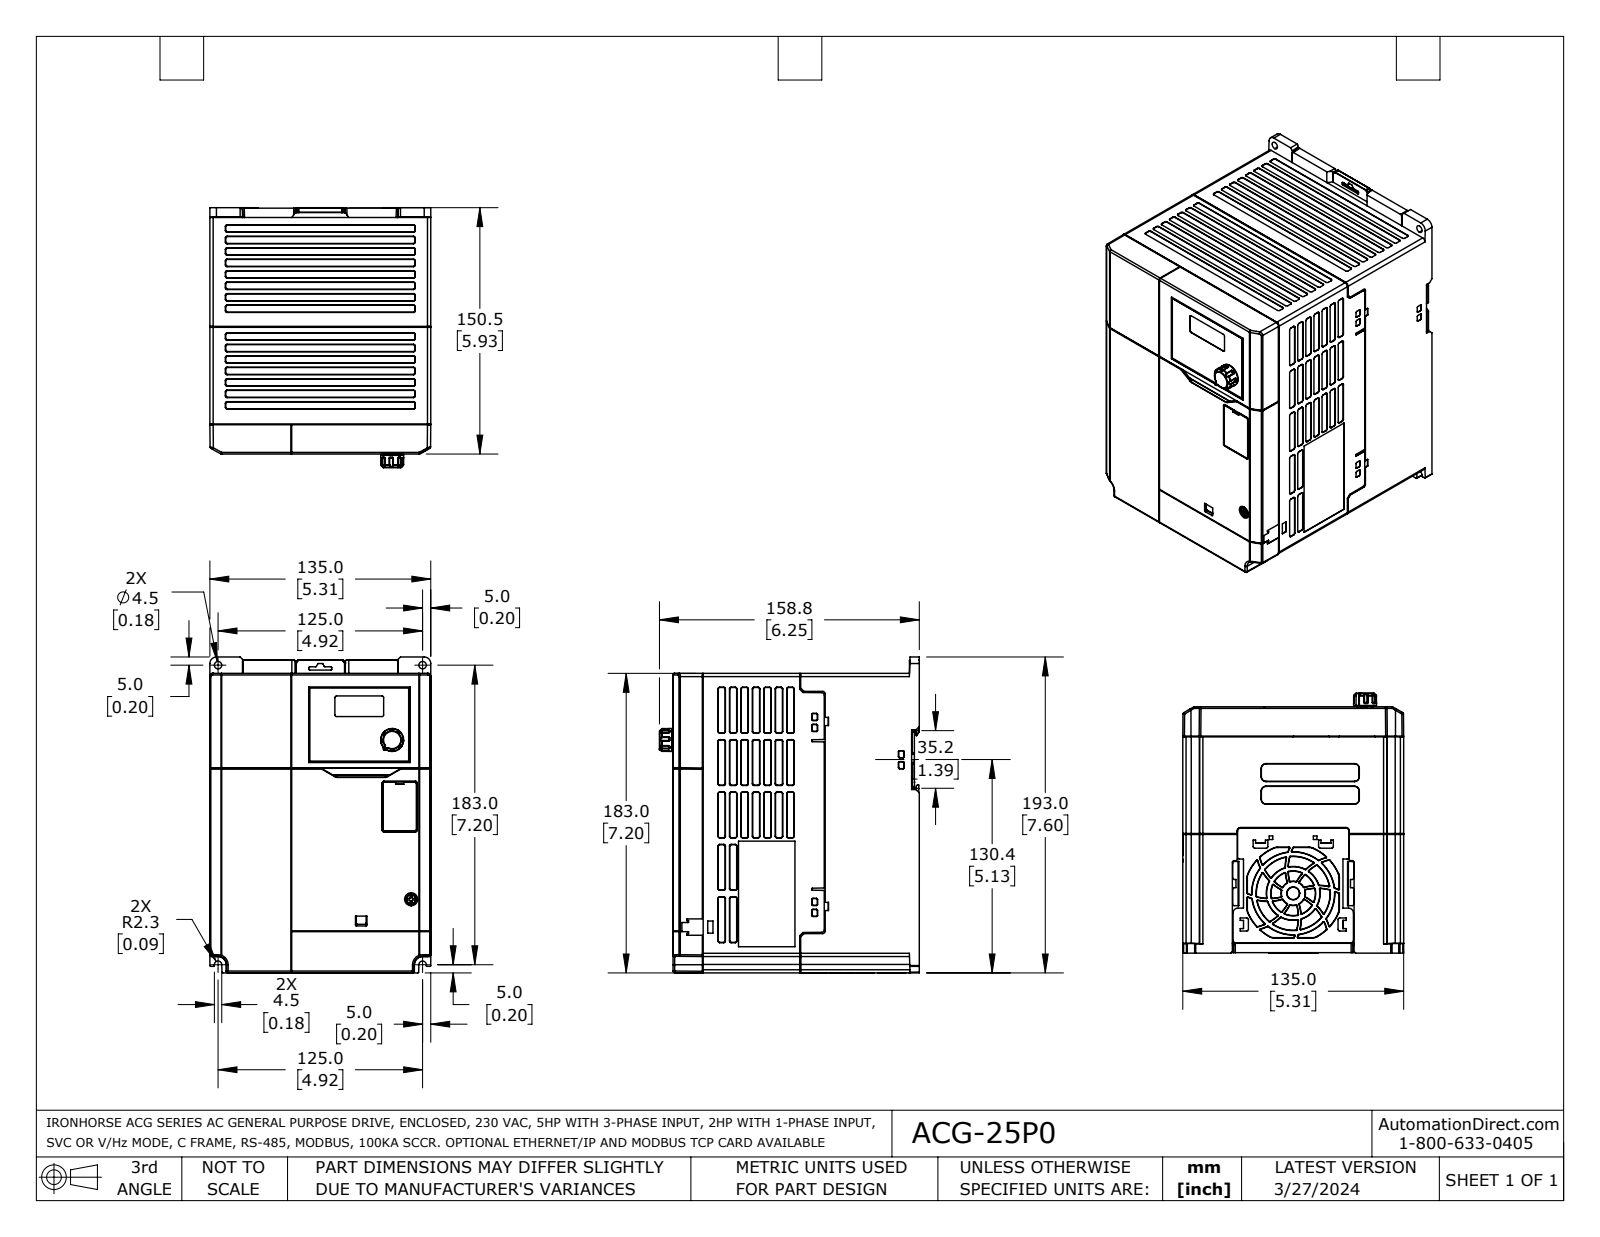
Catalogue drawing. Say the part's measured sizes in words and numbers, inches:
The part is named "ACG-35P0". Its 3-D file was written by "SolidWorks 2021 (AUTOMOTIVE_DESIGN)". It is 4 solids with 4834 faces: 2009 planar, 1108 cylindrical and 1717 other. Overall it measures 7.603 by 6.252 by 5.315 inches. Its volume is 73.09 cubic inches and its surface area 485.6 square inches. Round holes: 2 of diameter 0.177, 2 of diameter 0.472, 1 of diameter 0.039, 1 of diameter 0.276. Round bosses or shafts: 1 of diameter 0.551, 1 of diameter 0.543, 1 of diameter 0.236. Partial cylindrical surfaces (rounded edges, fillets, slot ends): 340 of radius 0.008, 254 of radius 0.02, 79 of radius 0.039, 30 of radius 0.012, 23 of radius 0.079, 17 of radius 0.031, 6 of radius 0.059, 4 of radius 0.016. The main face-to-face distances are 0.404, 4.911, 4.508, 5.642, 5.807, 5.083, 0.724, 0.165, 4.918, 5.315. The hole center spacings are 0.273, 0.276, 1.943, 1.944, 2.206, 3.675, 3.858, 3.858.
